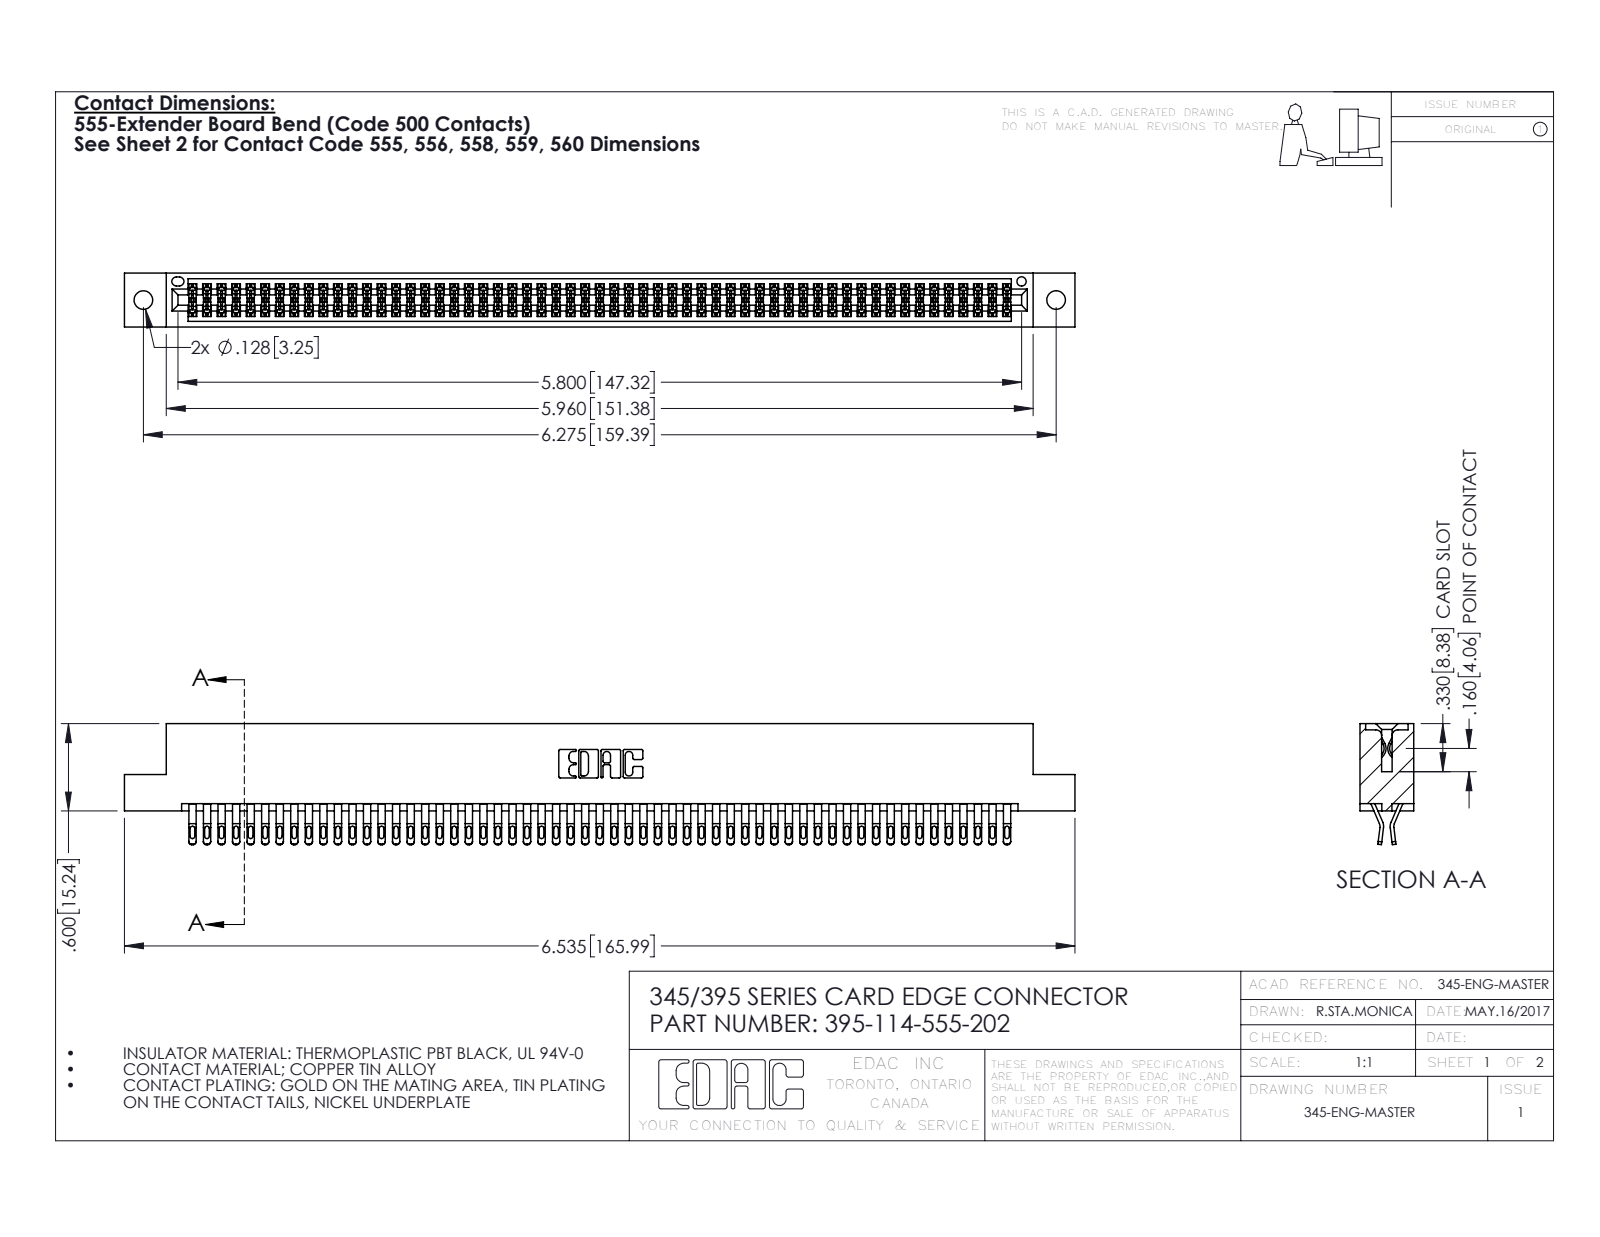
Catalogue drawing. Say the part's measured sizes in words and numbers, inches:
The part is named "395-114-555-202; 345-292-001_555 Tail; 345 Part_Flush Mounting Lugs - 0.128 Dia". Its 3-D file was written by "SolidWorks 2016 (CONFIG_CONTROL_DESIGN)". It is 115 solids with 6510 faces: 3614 planar, 2896 cylindrical and 0 other. Overall it measures 6.535 by 0.832 by 0.37 inches. Its volume is 1.01 cubic inches and its surface area 39.75 square inches. Round holes: 2 of diameter 0.128, 1 of diameter 0.064. Partial cylindrical surfaces (rounded edges, fillets, slot ends): 285 of radius 0.016, 228 of radius 0.02, 171 of radius 0.006, 22 of radius 0.01, 6 of radius 0.007, 6 of radius 0.031, 3 of radius 0.026, 2 of radius 0.01. The main face-to-face distances are 0.298, 0.072, 0.025, 0.37, 0.2, 0.098, 0.272, 0.225, 0.175, 0.149. The hole center spacings are 0.27, 6.039, 6.275.
